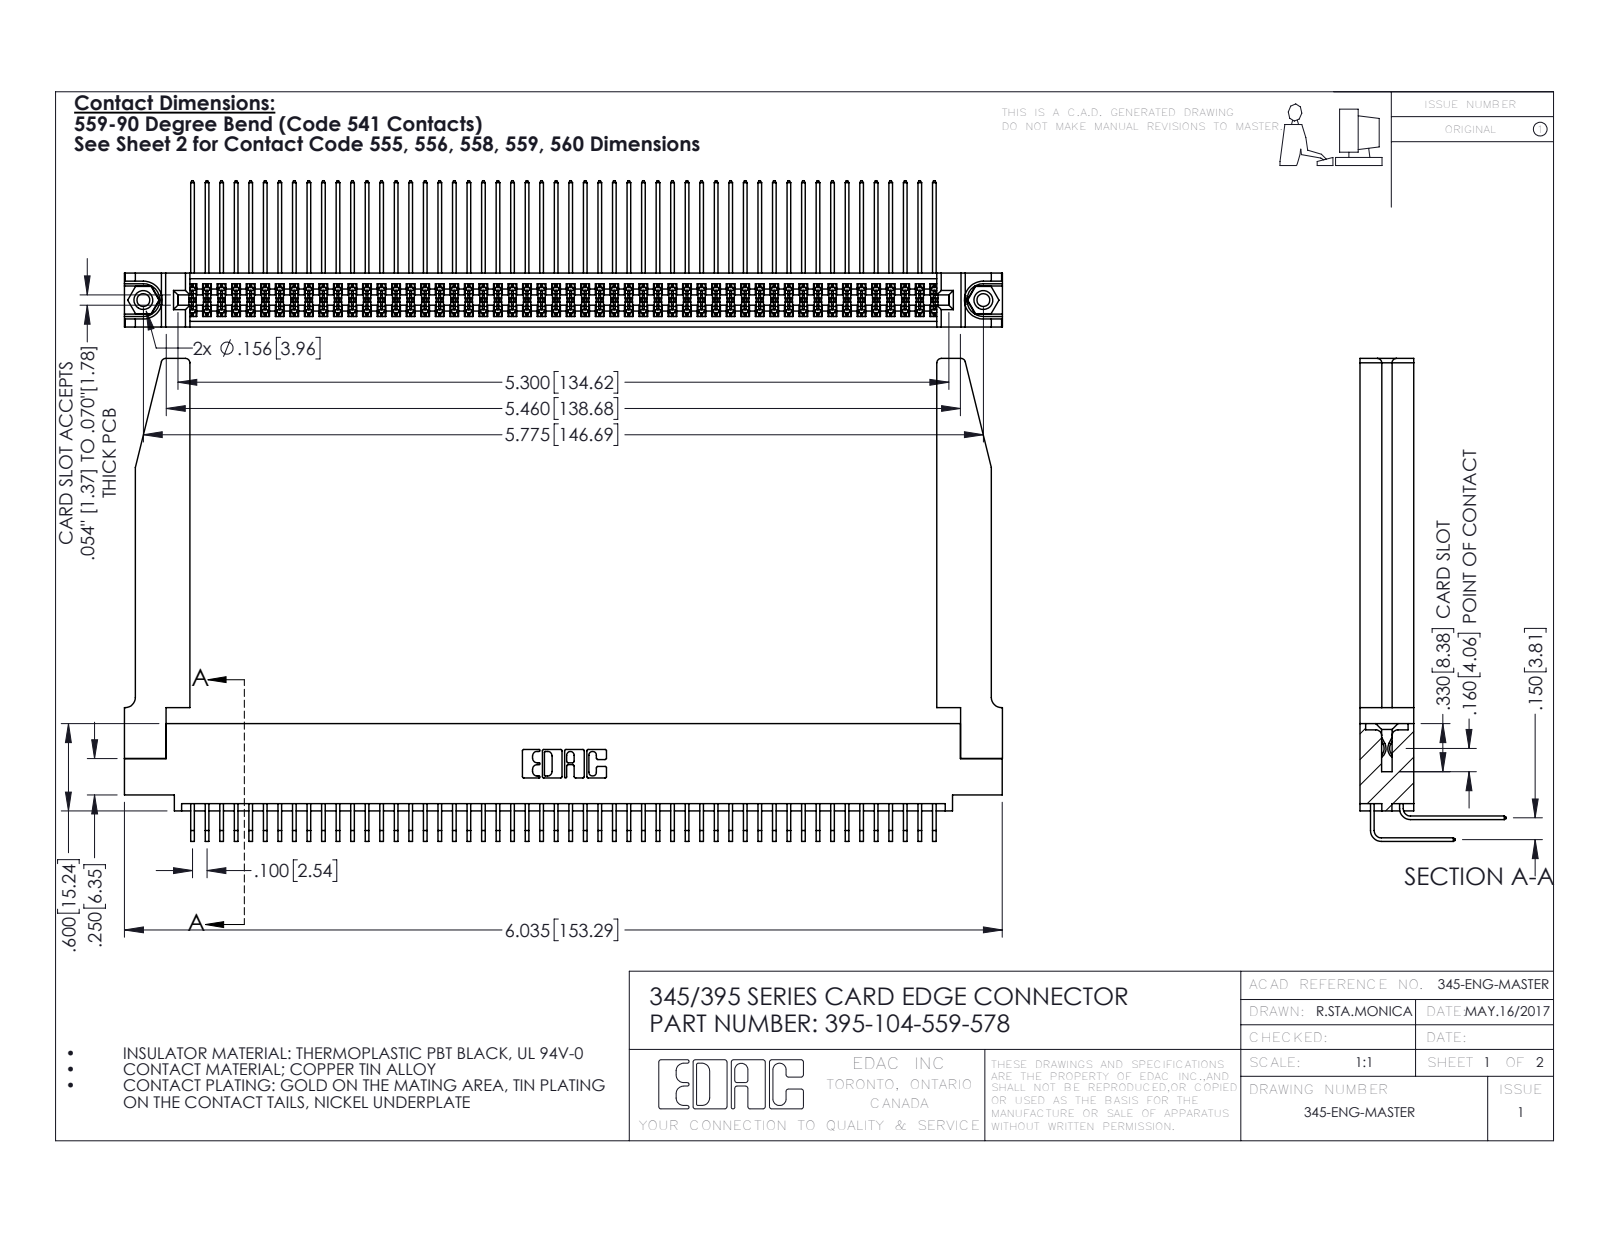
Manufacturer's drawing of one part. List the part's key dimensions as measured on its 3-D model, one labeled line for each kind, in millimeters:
Part name (STEP PRODUCT): 345-220-078_345-220-078; 345-292-001_559 Tail - 2; 345-250-001_345-250-001-102; 345-292-001_558 559 Tail - 1 (+2 more)
STEP written by: SolidWorks 2016 (CONFIG_CONTROL_DESIGN)
Units: millimetres
Bodies: 109 solids, 5772 faces (3866 planar, 1854 cylindrical, 52 other)
Overall size (bounding box): 153.3 × 84.3 × 25.5
Volume: 23 290 mm³ · Surface area: 32 880 mm²
Round holes (diameter × count): ⌀2.3 ×2, ⌀3.2 ×2, ⌀4 ×2, ⌀1.6 ×1
Round bosses / shafts (diameter × count): ⌀3.9 ×2
Partial cylindrical surfaces — rounded edges, fillets, slot ends (radius × count): R0.2 ×156, R0.3 ×22, R0.8 ×8, R0.2 ×6, R0.8 ×6, R0.7 ×3, R0.4 ×2, R0.5 ×2
Main face-to-face distances: 1.8, 7.6, 9.4, 2.5, 6.9, 0.6, 5.1, 5.7, 4.4, 3.8
Hole centre spacings: 6.9, 140.7, 146.7
